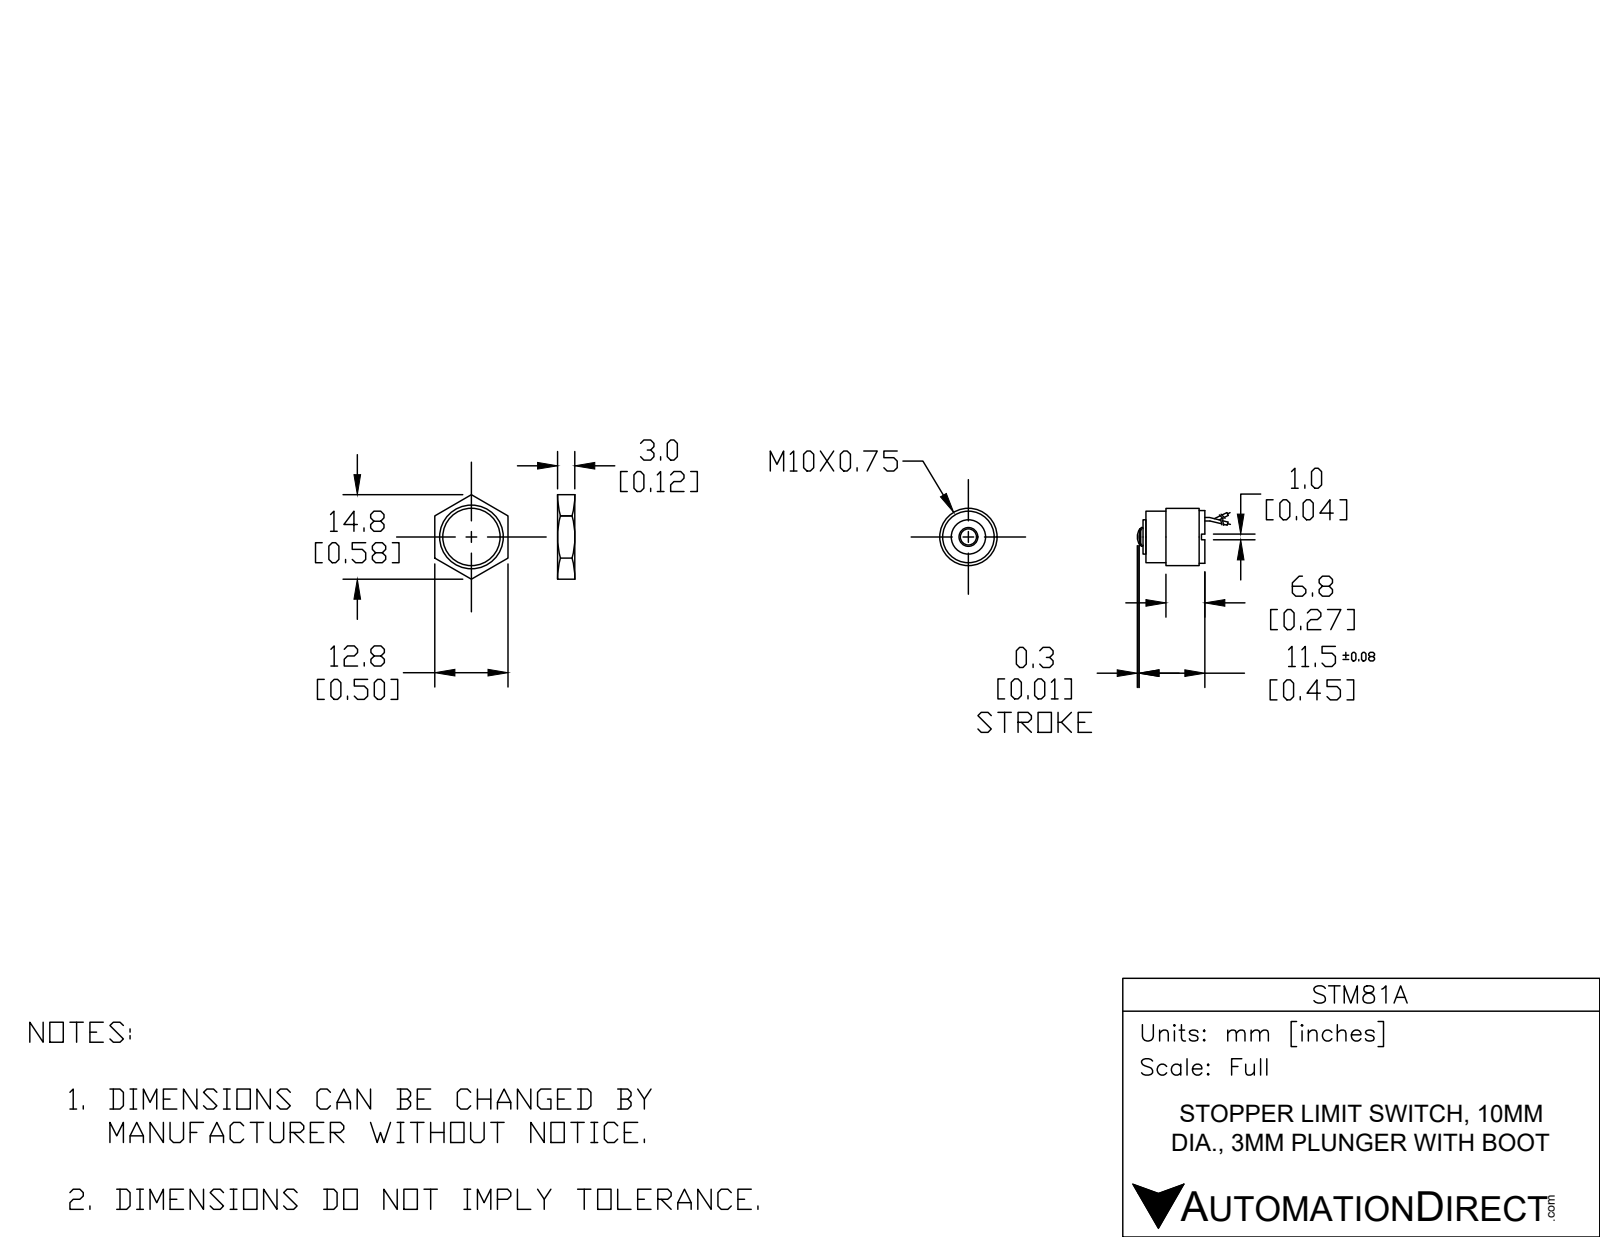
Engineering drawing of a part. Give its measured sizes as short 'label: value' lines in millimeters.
written by: Spatial InterOp 3D (CONFIG_CONTROL_DESIGN)
unit: mm
bodies: 1 solid, 52 faces (13 planar, 30 cylindrical, 9 other)
size: 21.8 × 10 × 10
volume: 711 mm³; area: 651 mm²
bosses: 2× ⌀0.6, 1× ⌀10, 1× ⌀9, 1× ⌀8.5, 1× ⌀6, 1× ⌀2.8
face distances: 10.3, 10.5, 0.5, 10.8, 1, 9.8, 9.5, 9.3, 0.4, 10.2
